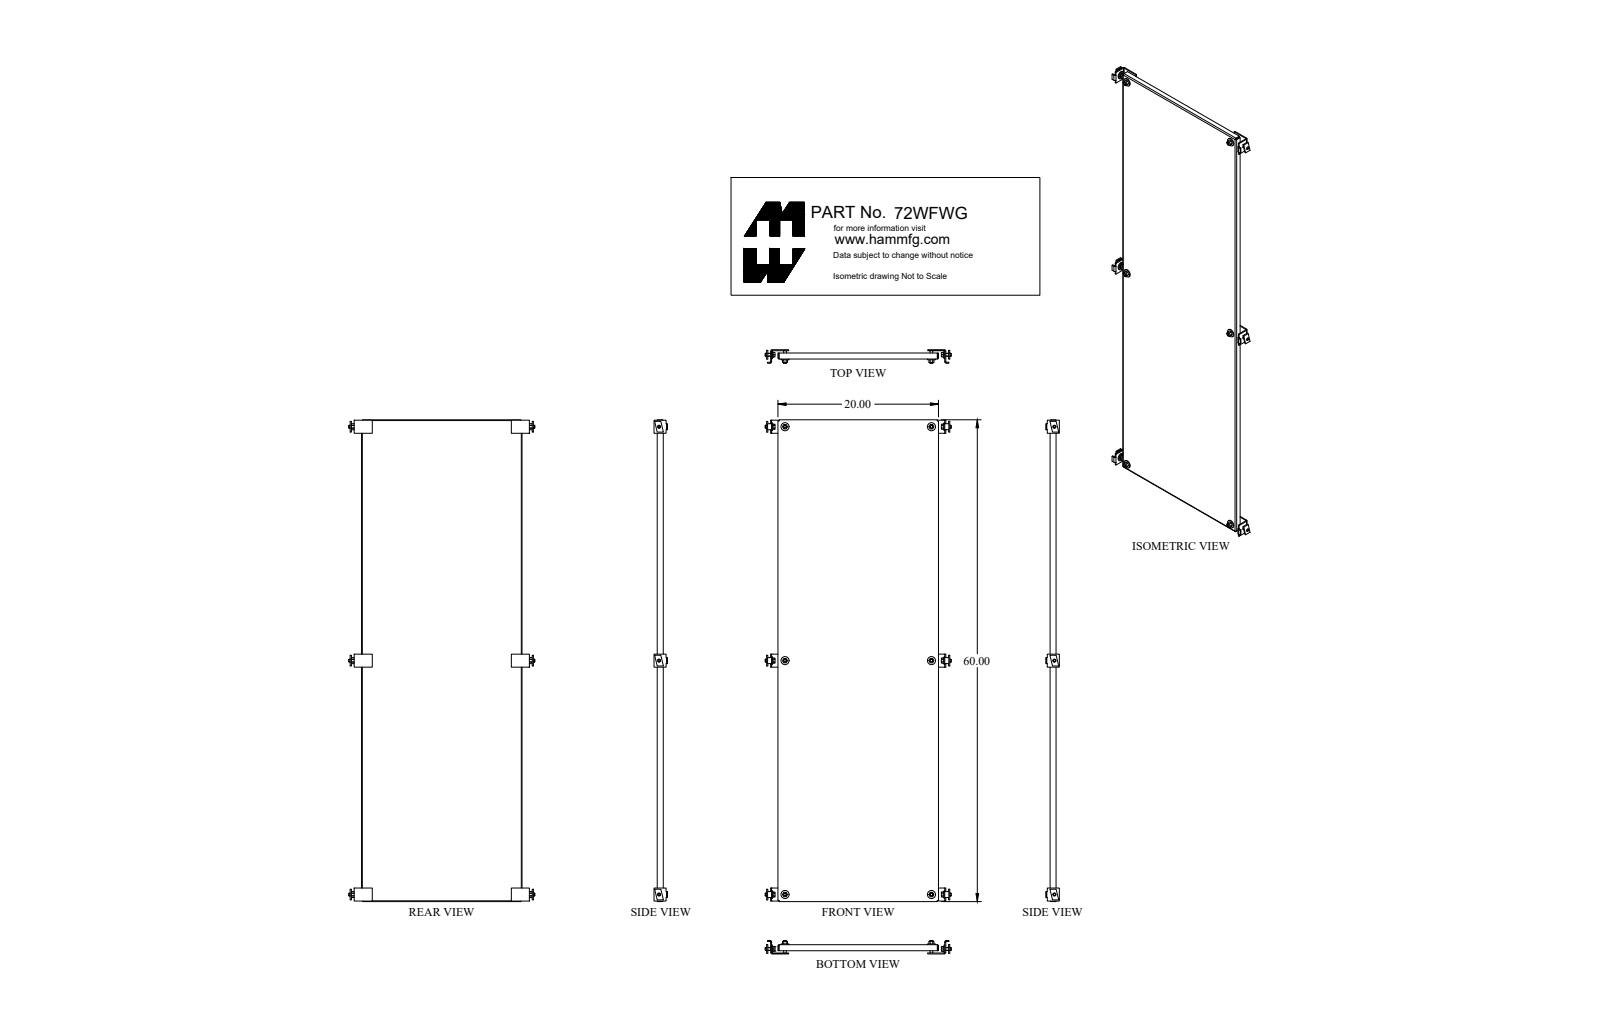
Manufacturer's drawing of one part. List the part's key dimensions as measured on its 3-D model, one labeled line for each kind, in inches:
Part name (STEP PRODUCT): 72WFWG_Default
STEP written by: SolidWorks 2018 (CONFIG_CONTROL_DESIGN)
Units: inches
Bodies: 13 solids, 270 faces (130 planar, 92 cylindrical, 48 other)
Overall size (bounding box): 60 × 22.582 × 1.687
Volume: 128.7 in³ · Surface area: 2 705 in²
Round holes (diameter × count): ⌀0.563 ×6, ⌀0.437 ×3
Round bosses / shafts (diameter × count): ⌀0.65 ×6, ⌀0.375 ×6, ⌀0.33 ×6
Partial cylindrical surfaces — rounded edges, fillets, slot ends (radius × count): R0.048 ×4, R0.06 ×4, R0.143 ×4, R0.185 ×4
Main face-to-face distances: 0.095, 19.905, 19.81, 20, 0.125, 59.905, 1.032, 0.937, 1.157, 1.062
Hole centre spacings: 29.125, 34.37, 18.25, 29.13, 58.25, 61.041, 58.26
